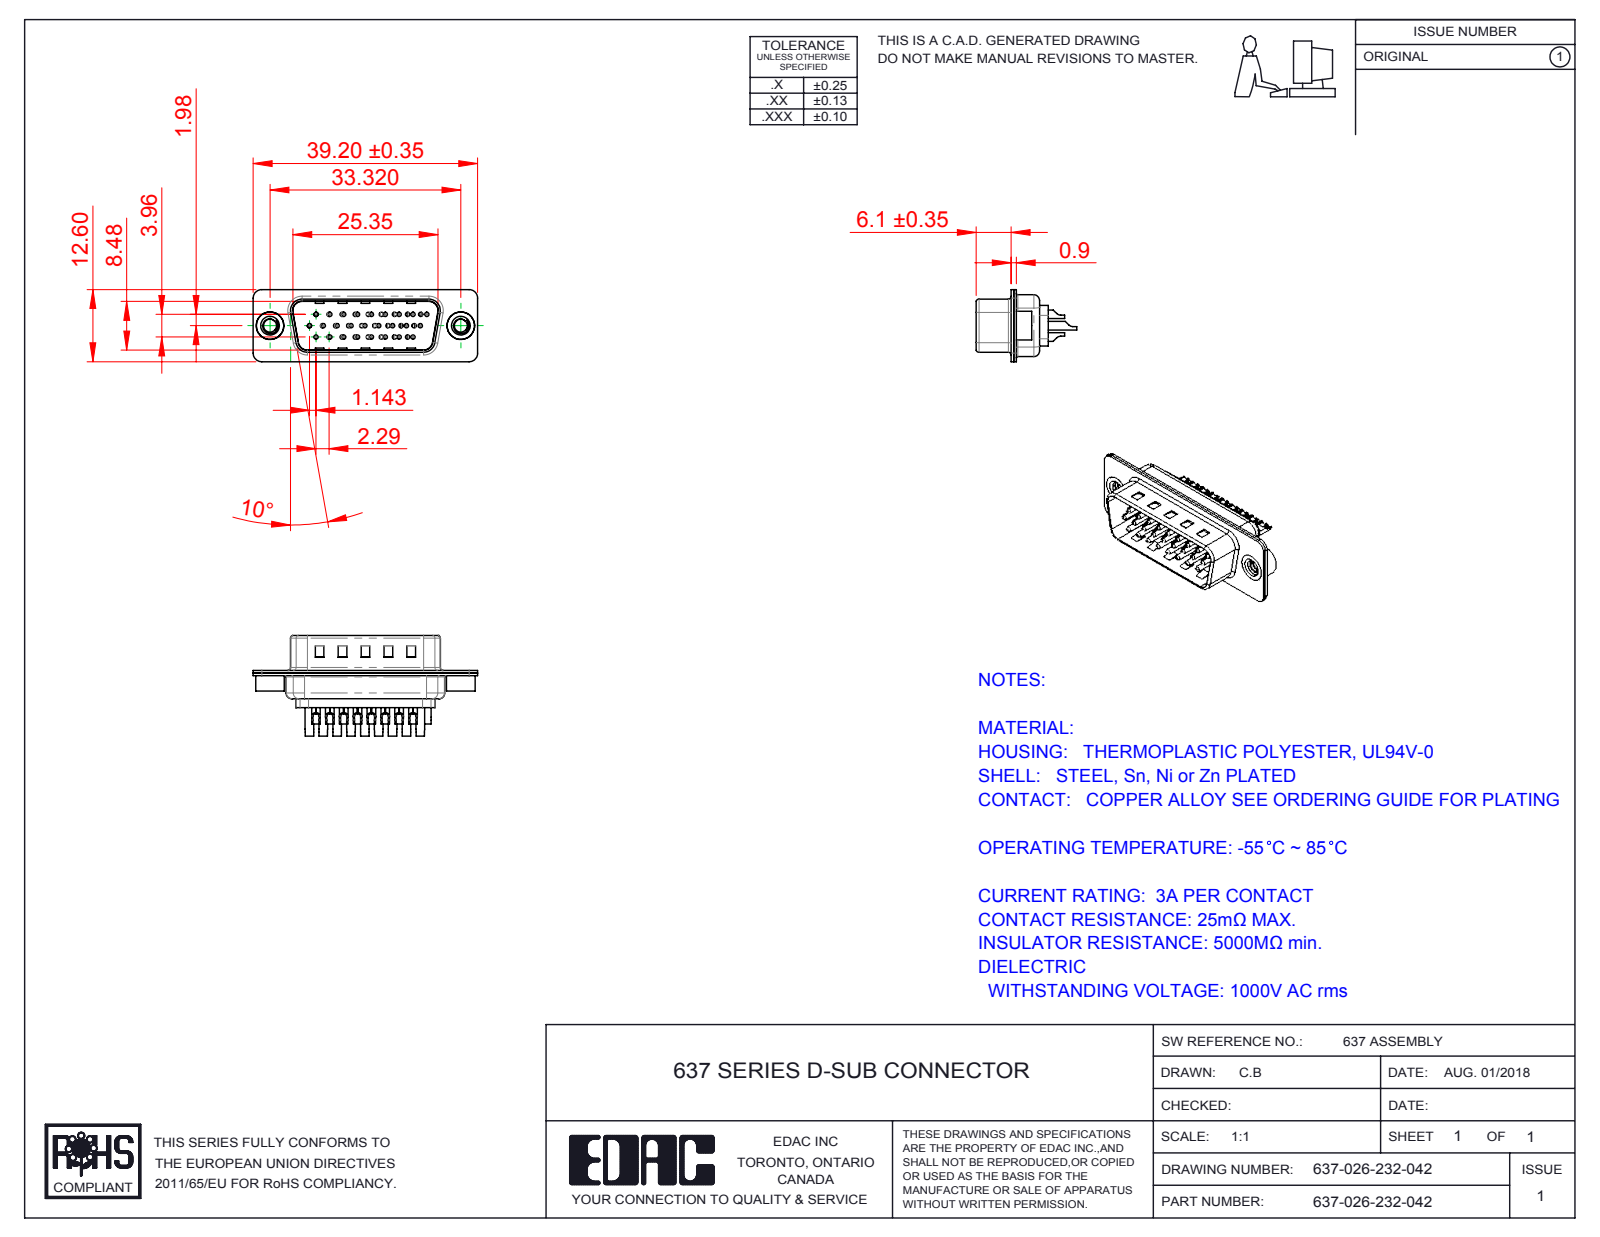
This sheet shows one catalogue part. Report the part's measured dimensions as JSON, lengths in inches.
{"part_name": "637-026-232-042; 637 Shell Rear_26 Contacts; 637 Contact Row 1_32; 637 Contact Row 2_32 (+4 more)", "step_written_by": "SolidWorks 2016 (CONFIG_CONTROL_DESIGN)", "units": "inches", "bodies": {"solids": 31, "faces": 2004, "planar": 503, "cylindrical": 887, "other": 614}, "overall_size": [1.543, 0.691, 0.496], "volume_in3": 0.113, "surface_area_in2": 10.74, "round_holes": [[0.063, 49], [0.014, 26], [0.043, 26], [0.03, 23], [0.079, 23], [0.089, 2], [0.157, 2], [0.189, 2]], "round_bosses_or_shafts": [[0.079, 26], [0.059, 26], [0.03, 26], [0.197, 2], [0.193, 2]], "partial_cylinders_radius": [[0.059, 16], [0.079, 12], [0.02, 8], [0.039, 7], [0.01, 4], [0.022, 4], [0.028, 4], [0.037, 4]], "face_to_face_distances": [0.018, 0.016, 0.035, 0.334, 0.028, 0.35, 0.012, 0.179, 0.041, 0.046], "hole_center_spacings": [0.156, 0.09, 0.18, 0.238, 0.09, 0.324, 0.27, 0.413]}
